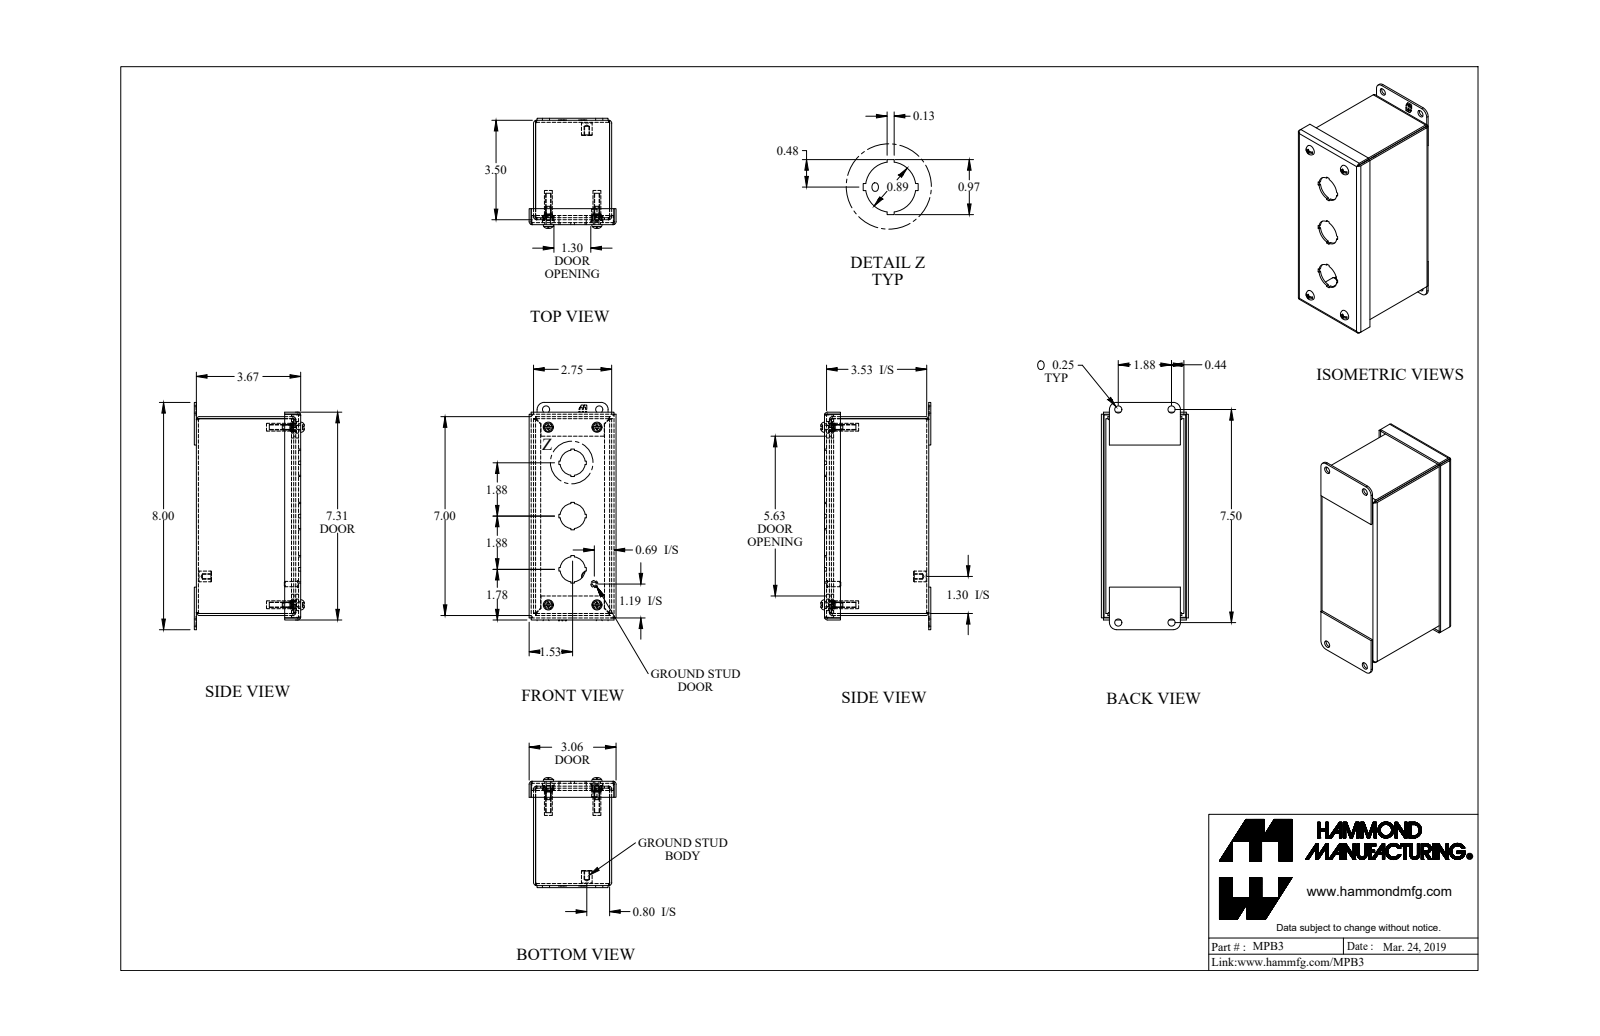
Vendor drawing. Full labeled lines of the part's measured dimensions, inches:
Part name (STEP PRODUCT): MPB3
STEP written by: SolidWorks 2018 (AUTOMOTIVE_DESIGN)
Units: inches
Bodies: 19 solids, 603 faces (395 planar, 152 cylindrical, 56 other)
Overall size (bounding box): 8 × 3.871 × 3.063
Volume: 11.14 in³ · Surface area: 293.7 in²
Round holes (diameter × count): ⌀0.25 ×8, ⌀0.159 ×4, ⌀0.406 ×4, ⌀0.886 ×3, ⌀0.156 ×1
Round bosses / shafts (diameter × count): ⌀0.39 ×4, ⌀0.275 ×4, ⌀0.19 ×4, ⌀0.148 ×4, ⌀0.375 ×1, ⌀0.25 ×1, ⌀0.188 ×1
Partial cylindrical surfaces — rounded edges, fillets, slot ends (radius × count): R0.036 ×12, R0.108 ×12, R0.16 ×4, R0.171 ×4, R0.25 ×4
Main face-to-face distances: 0.072, 0.072, 2.678, 3.6, 3.672, 2.75, 2.606, 3.528, 6.928, 3.5
Hole centre spacings: 1.711, 0.63, 1.898, 3.241, 3.865, 6.25, 6.48, 6.876
